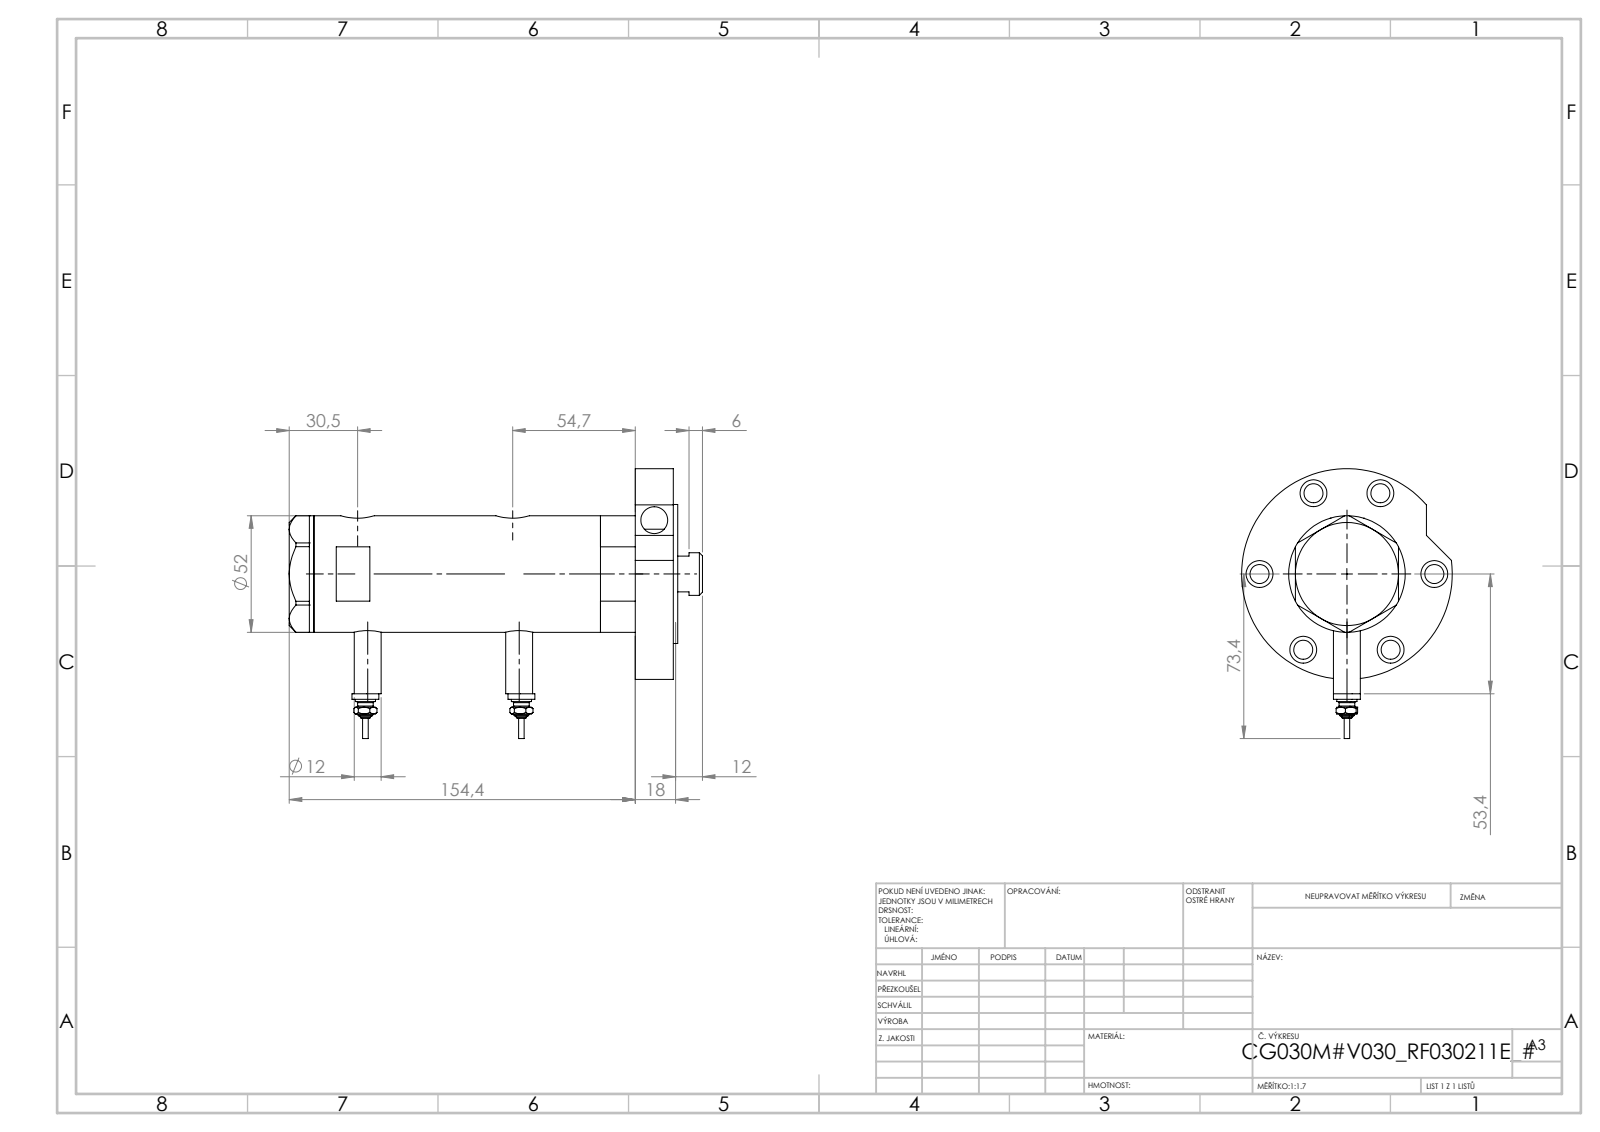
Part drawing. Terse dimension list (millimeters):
name: V270CG_MIDDLE; V270CG_FRONT; V270CG_SWITCH; V270CG_RF211E (+2 more)
written by: SolidWorks 2019 (CONFIG_CONTROL_DESIGN)
unit: mm
bodies: 7 solids, 290 faces (106 planar, 110 cylindrical, 74 other)
size: 179.02 × 105.3 × 94
volume: 404 117 mm³; area: 100 431 mm²
holes: 7× ⌀12, 6× ⌀8.5, 2× ⌀5, 2× ⌀9.73, 2× ⌀12.5, 2× ⌀15, 1× ⌀6.5, 1× ⌀20, 1× ⌀21.5, 1× ⌀30, 1× ⌀33, 1× ⌀40
bosses: 3× ⌀12, 2× ⌀9, 2× ⌀7, 2× ⌀4.34, 2× ⌀2.4, 1× ⌀94, 1× ⌀62, 1× ⌀52
face distances: 17, 135.45, 152.45, 2, 154.45, 19, 23.81, 111.64, 128.64, 130.64
hole spacings: 39, 2.9, 4.5, 43.34, 56.75, 59.65, 61.25, 64.15
